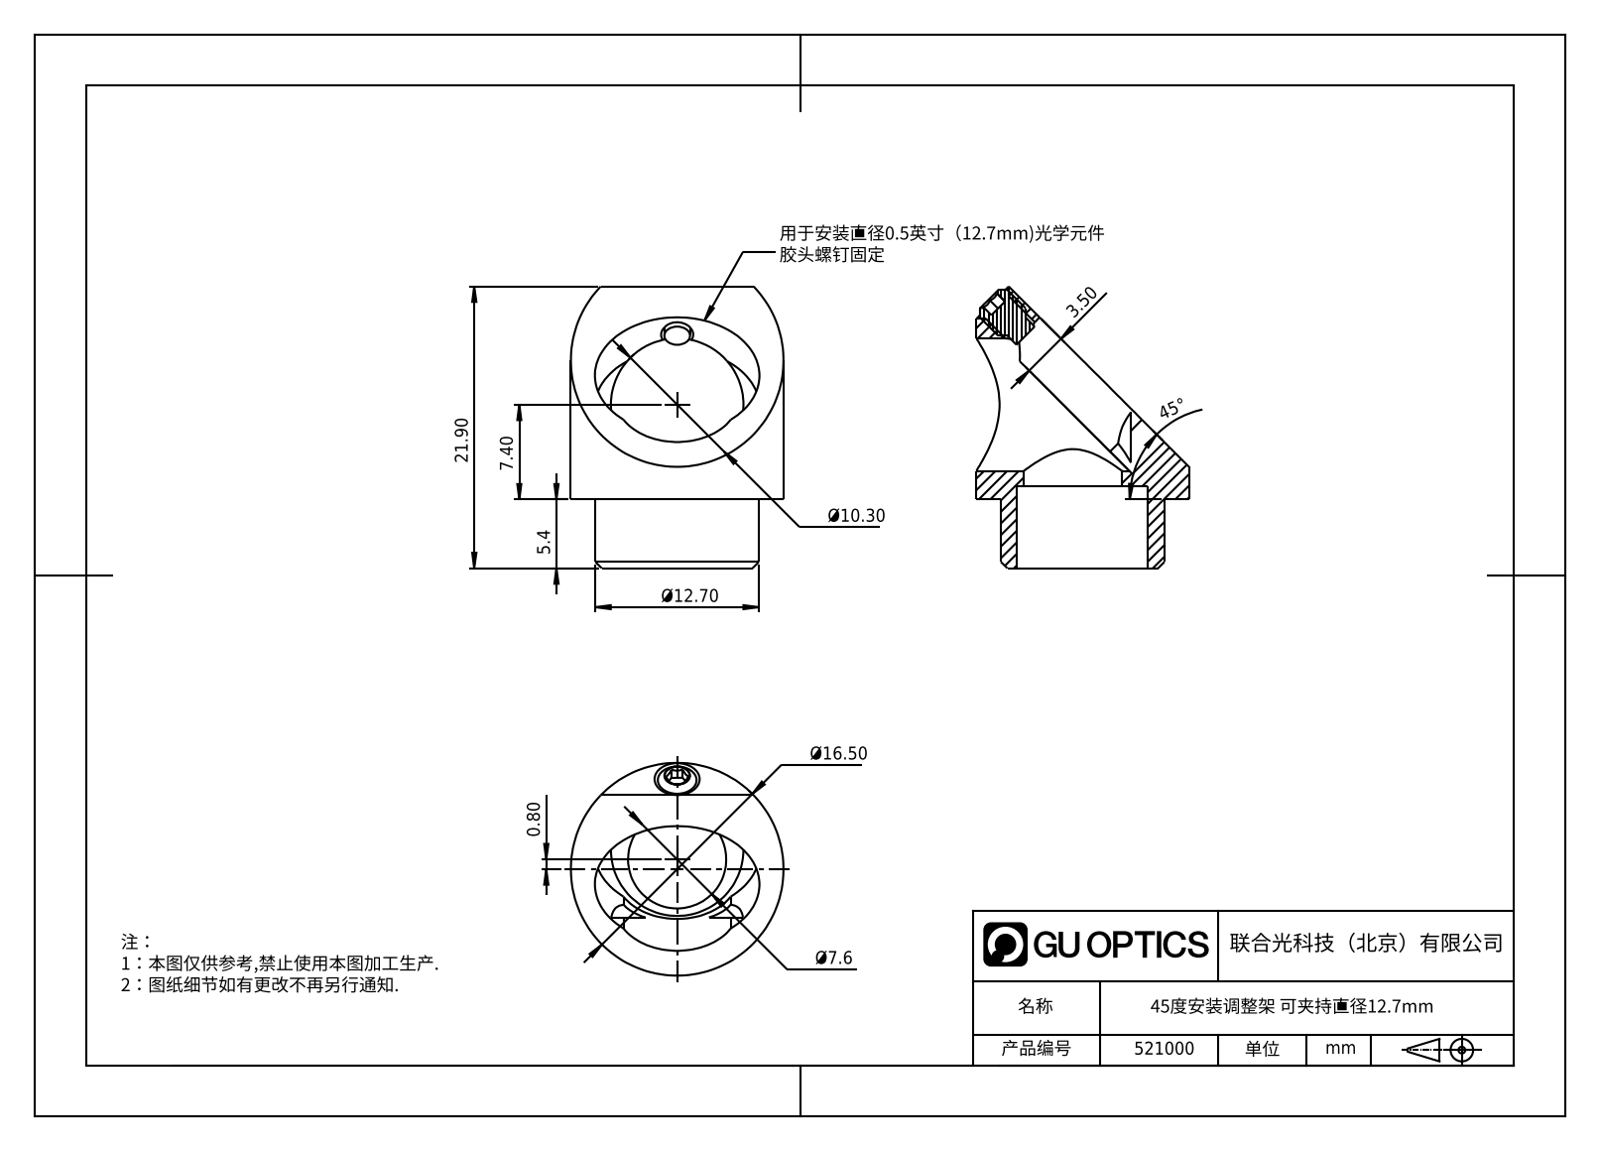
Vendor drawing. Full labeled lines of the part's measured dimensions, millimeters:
Part name (STEP PRODUCT): 1.3.1.21-ZZT-Z0.5_45度透镜安装座
STEP written by: SolidWorks 2021 (CONFIG_CONTROL_DESIGN)
Units: millimetres
Bodies: 0 solids, 43 faces (14 planar, 21 cylindrical, 8 other)
Overall size (bounding box): 21.87 × 16.51 × 16.51
Round holes (diameter × count): ⌀2.5 ×1, ⌀7.62 ×1, ⌀10.16 ×1, ⌀10.29 ×1
Round bosses / shafts (diameter × count): ⌀16.51 ×1, ⌀12.9 ×1, ⌀3 ×1, ⌀2 ×1
Partial cylindrical surfaces — rounded edges, fillets, slot ends (radius × count): R4.76 ×1, R6.39 ×1
Main face-to-face distances: 1.02, 5.33, 6.35, 3.5, 1.5, 0.62, 1, 0.38
Hole centre spacings: 0.76
